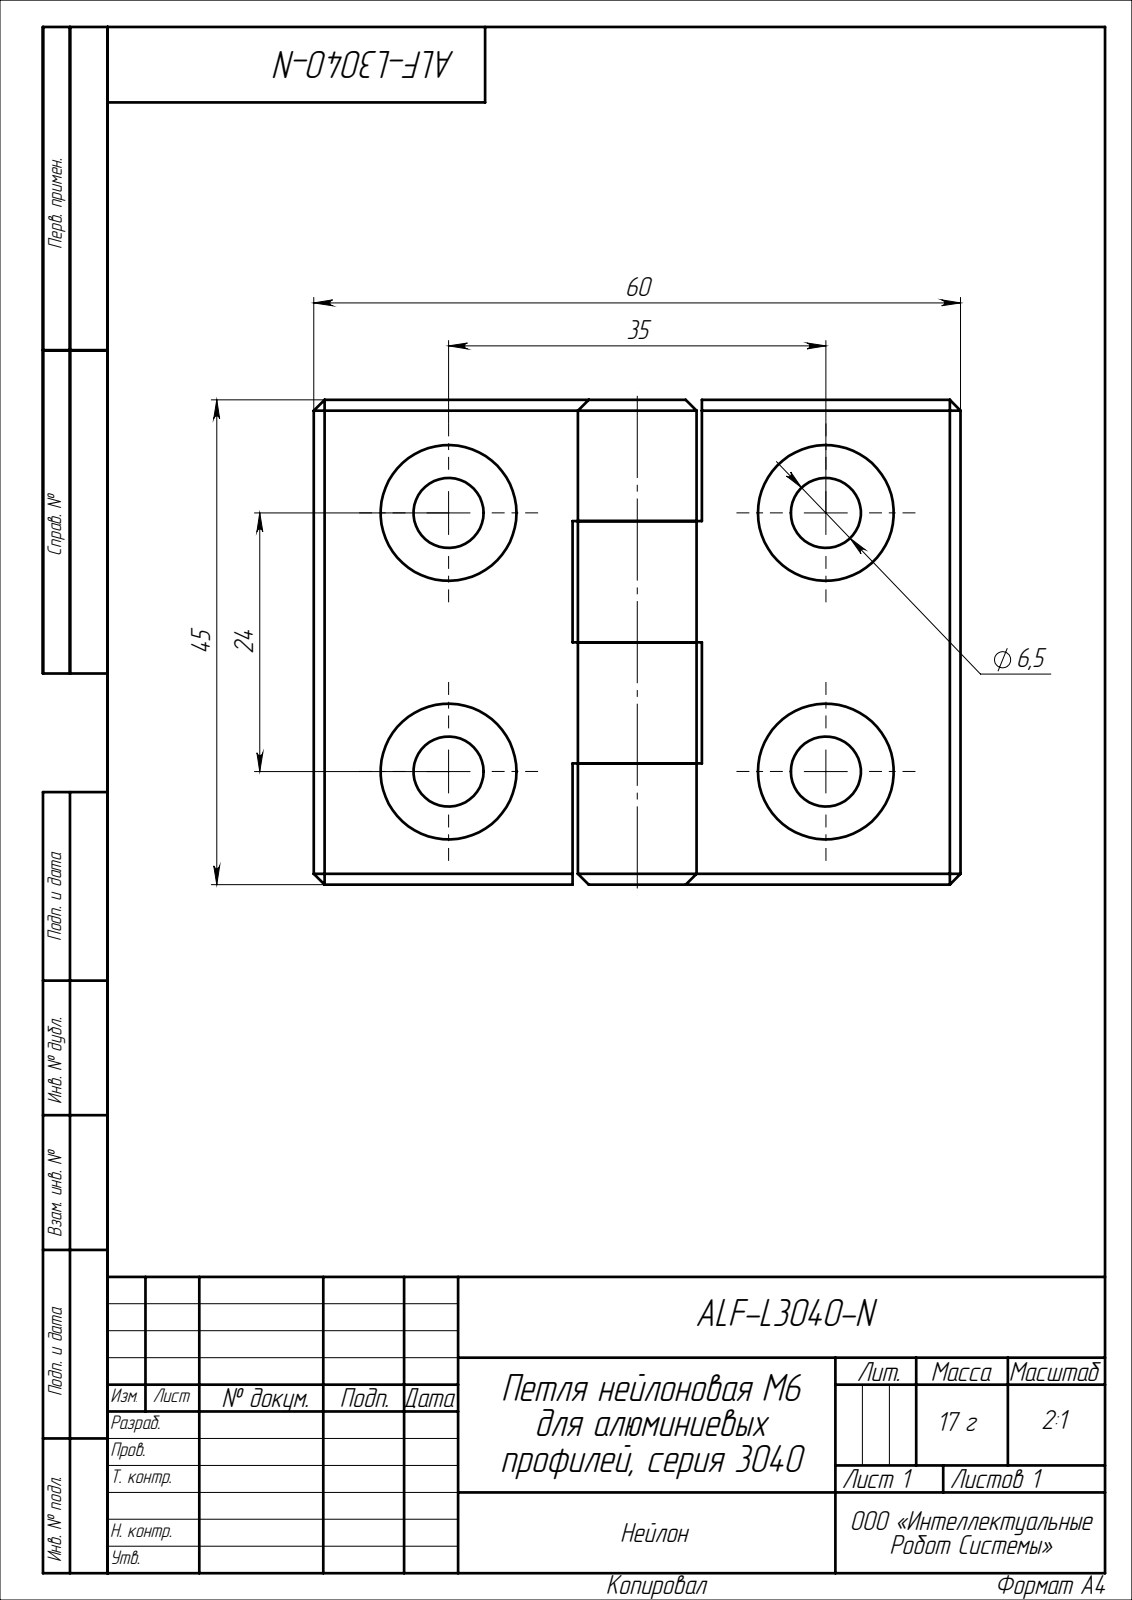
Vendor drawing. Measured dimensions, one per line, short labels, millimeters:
name: ALF-L3040-N
written by: SolidWorks 2022 (CONFIG_CONTROL_DESIGN)
unit: mm
bodies: 2 solids, 74 faces (44 planar, 20 cylindrical, 10 other)
size: 60 × 45 × 11
volume: 14 937 mm³; area: 7 733 mm²
holes: 4× ⌀6.5, 4× ⌀12.6
bosses: 1× ⌀11
face distances: 5.5, 11.25, 22.5, 33.75, 24, 36, 45, 60, 34.29, 12
hole spacings: 24, 35, 42.44
